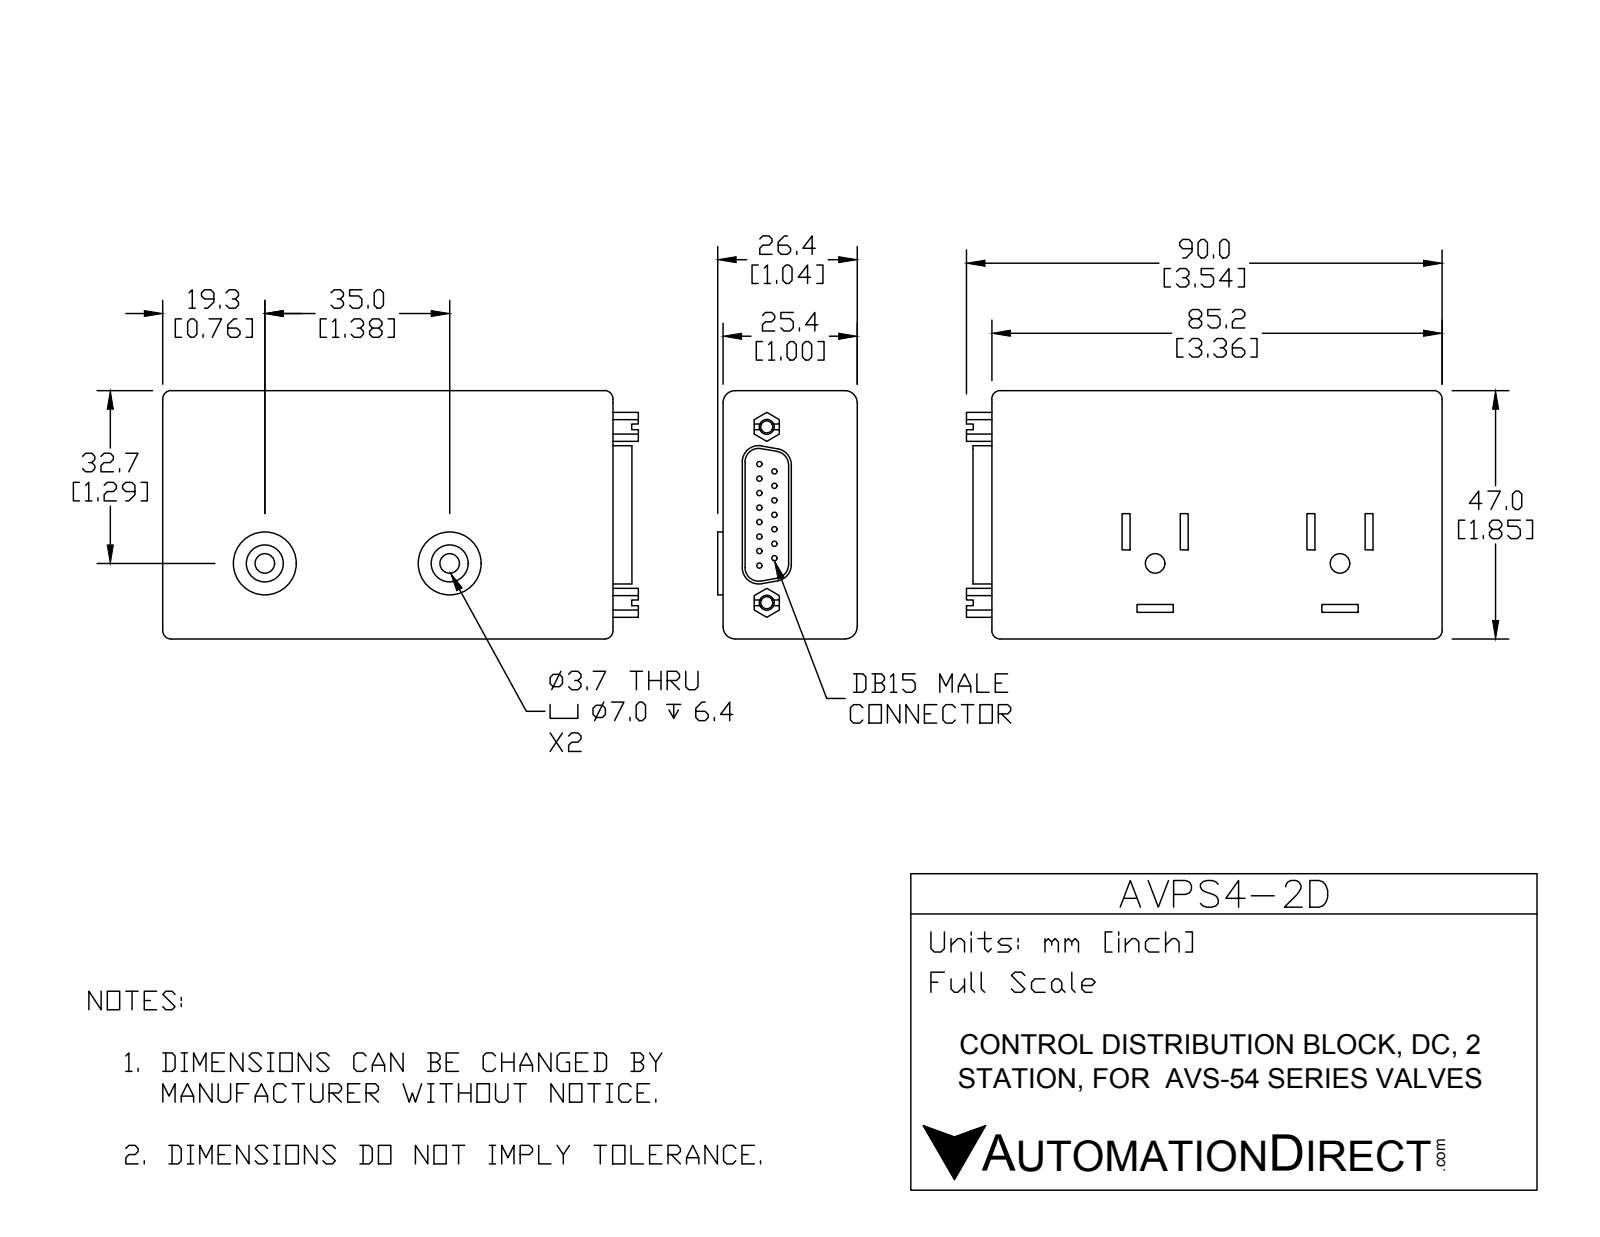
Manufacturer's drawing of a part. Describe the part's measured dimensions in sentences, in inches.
The part is named "AVPS4-2D". Its 3-D file was written by "SolidWorks 2016 (AUTOMOTIVE_DESIGN)". It is 1 solid with 173 faces: 93 planar, 68 cylindrical and 12 other. Overall it measures 3.545 by 1.85 by 1.04 inches. Its volume is 6.093 cubic inches and its surface area 25.94 square inches. Round holes: 2 of diameter 0.089, 2 of diameter 0.145, 2 of diameter 0.275. Round bosses or shafts: 15 of diameter 0.039, 2 of diameter 0.469. Partial cylindrical surfaces (rounded edges, fillets, slot ends): 6 of radius 0.062, 4 of radius 0.09, 4 of radius 0.102, 4 of radius 0.122, 2 of radius 0.063. The main face-to-face distances are 1, 1.85, 3.356, 0.059, 1.378, 0.123, 3.233, 0.433, 0.02, 0.04. The hole center spacings are 1.311, 1.378.
